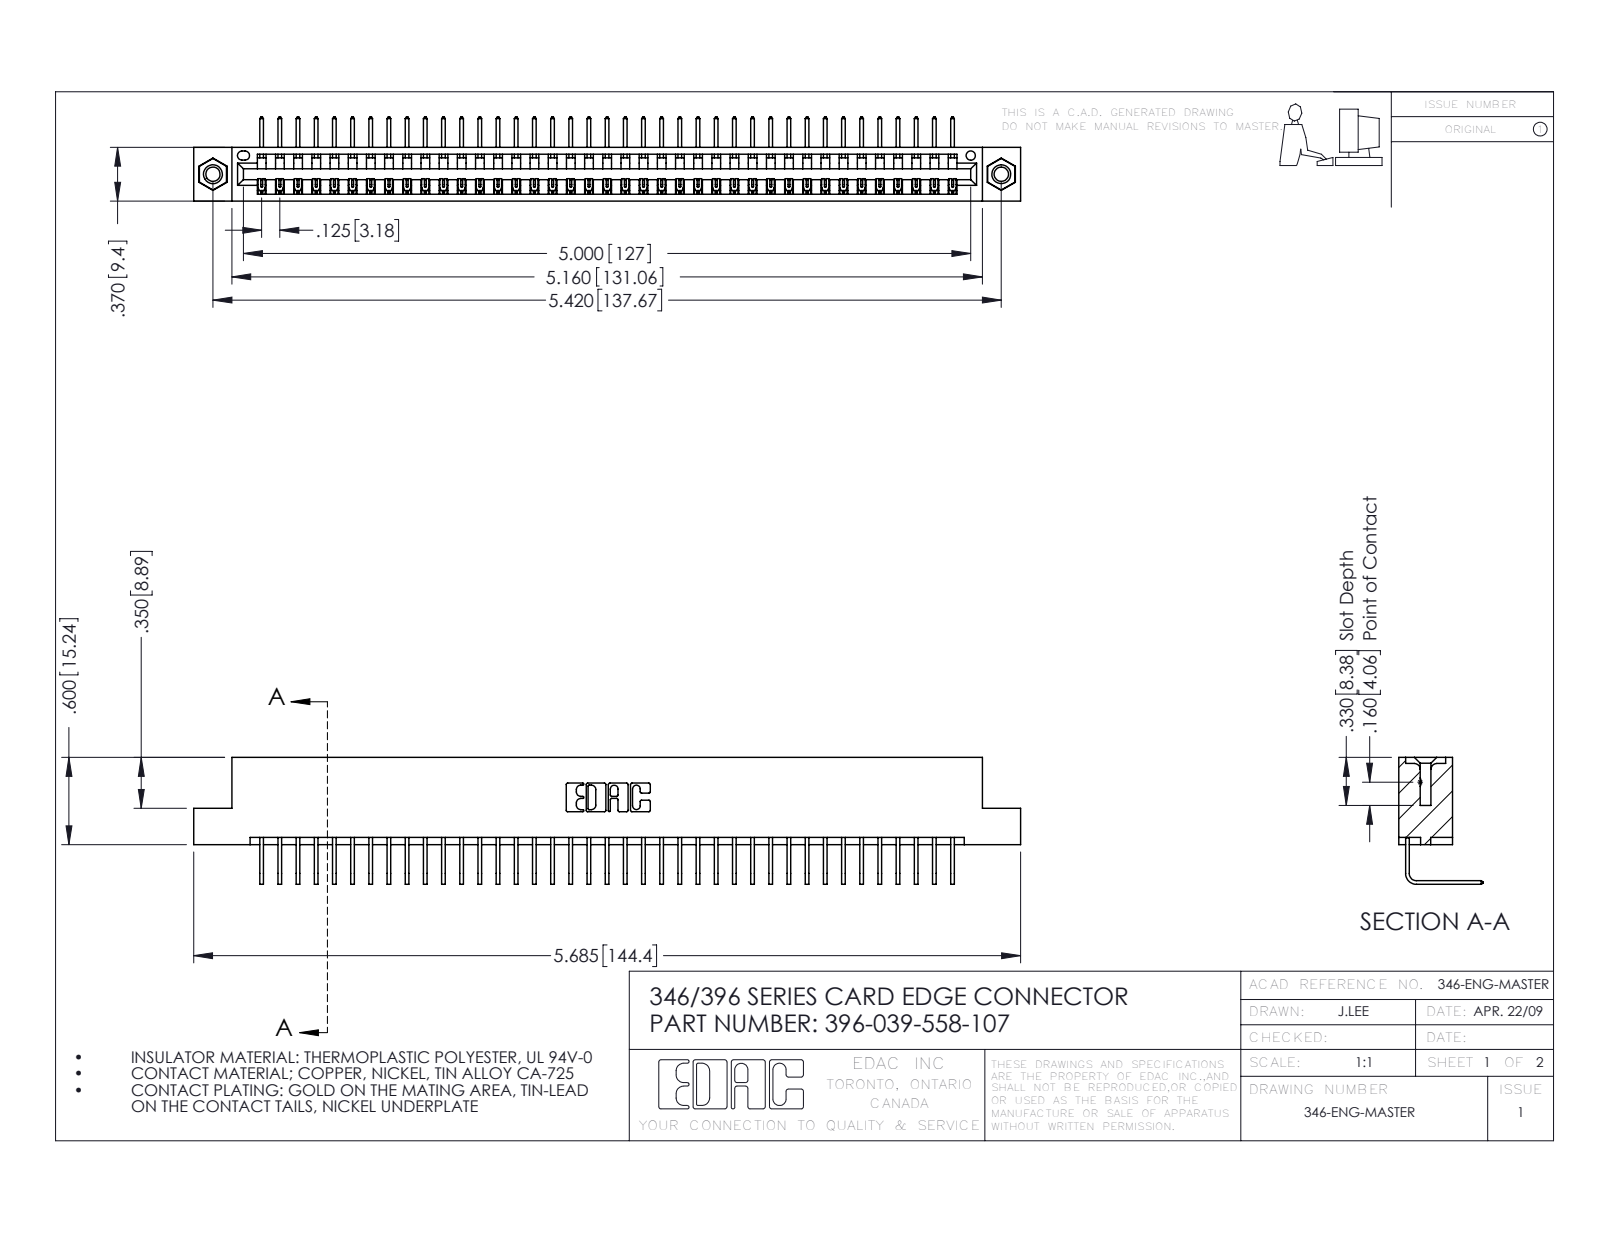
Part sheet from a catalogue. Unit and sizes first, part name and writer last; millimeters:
Units: millimetres
Overall size (bounding box): 144.4 × 22.2 × 14.7
Round holes (diameter × count): ⌀2.5 ×2, ⌀3.2 ×2, ⌀4 ×2, ⌀1.6 ×1
Round bosses / shafts (diameter × count): ⌀3.9 ×2
Partial cylindrical surfaces — rounded edges, fillets, slot ends (radius × count): R0.2 ×78, R0.3 ×22, R0.2 ×6, R0.8 ×6, R0.7 ×3, R0.8 ×2, R1 ×2, R0.4 ×1
Main face-to-face distances: 8.2, 1.2, 9.4, 6.4, 7.6, 0.6, 1.8, 3.8, 5.6, 2.5
Hole centre spacings: 6.2, 132.4, 137.7
Volume: 13 900 mm³ · Surface area: 18 170 mm²
Bodies: 42 solids, 2522 faces (1746 planar, 760 cylindrical, 16 other)
Part name (STEP PRODUCT): 345-250-001_345-250-005-103; 396-039-558-107; 345-292-001_558 Tail - 2; 346 Part_Flush Mounting Lugs - 0.156 Dia-TI
STEP written by: SolidWorks 2016 (CONFIG_CONTROL_DESIGN)
